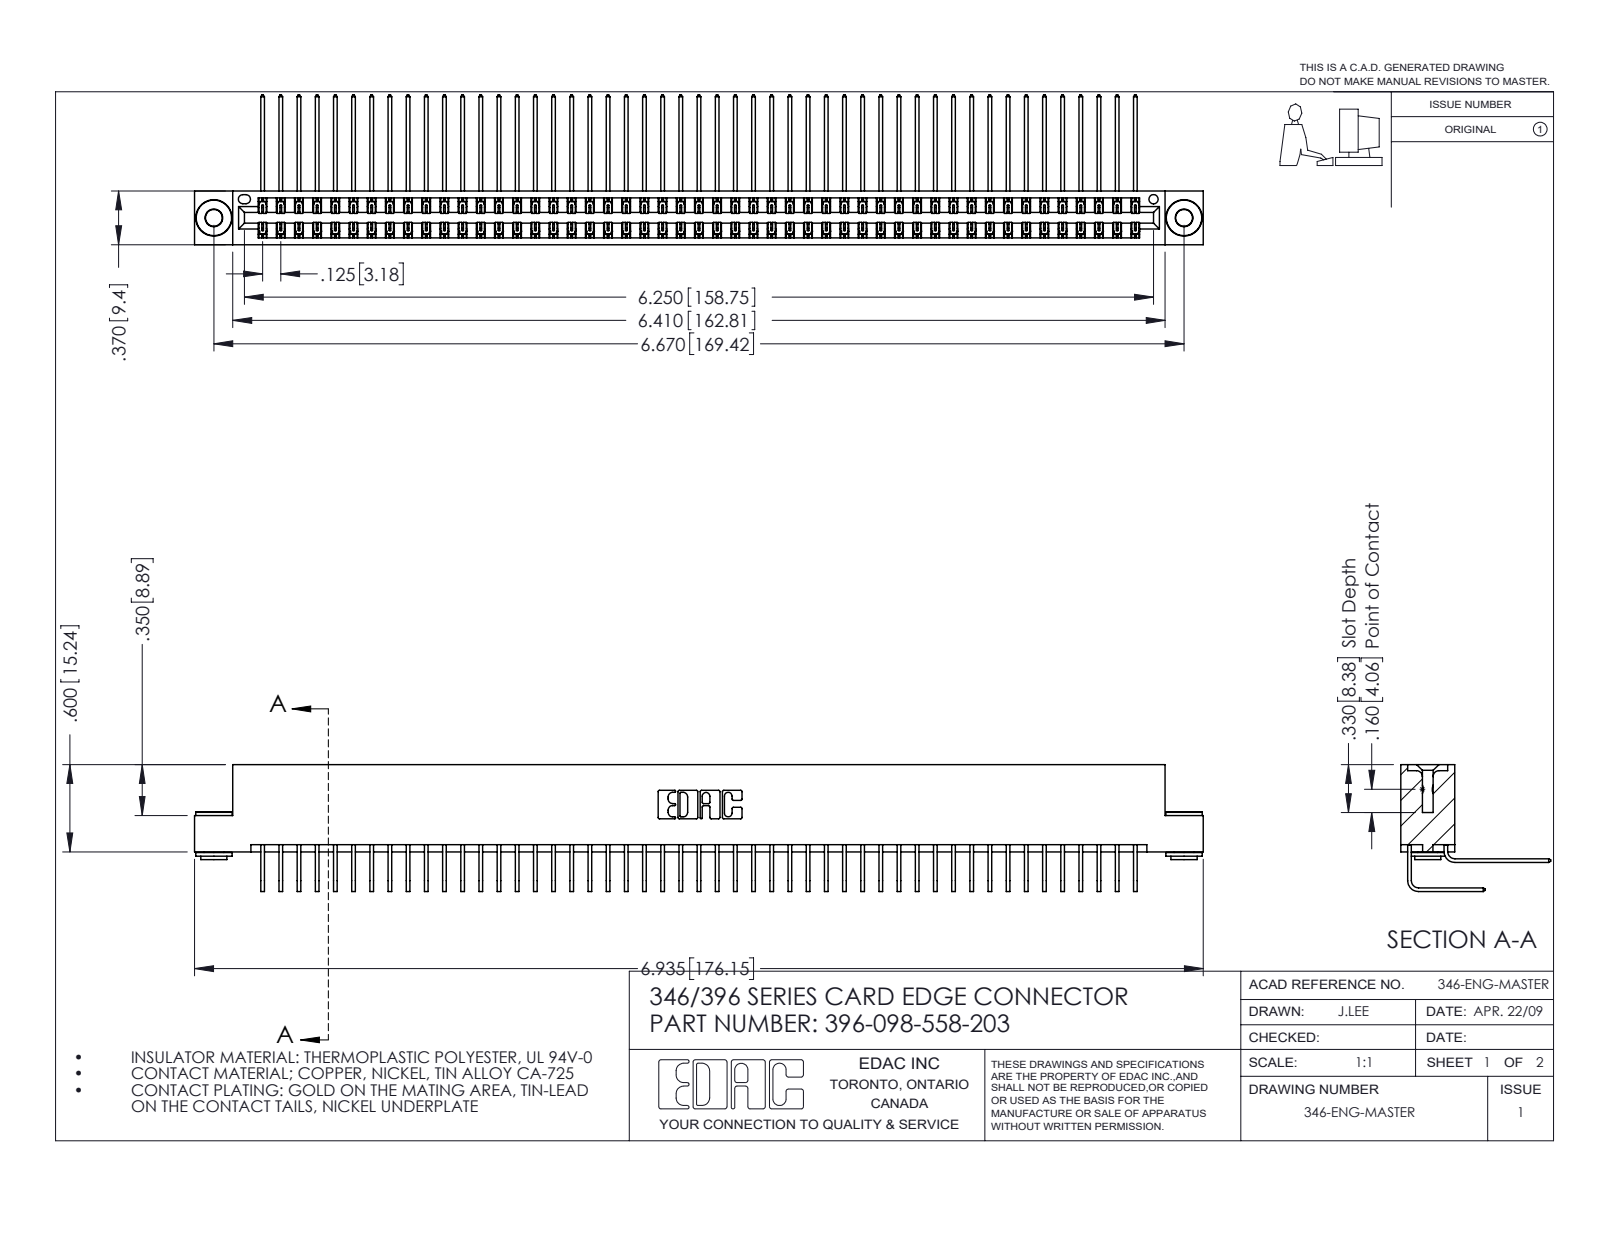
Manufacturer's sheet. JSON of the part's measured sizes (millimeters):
{"part_name": "346 Part_Flush Mounting Lugs - 0.156 Dia-TH; 345-292-001_558 Tail - 2; 345-292-001_558 559 Tail - 1; 345-250-002_345-250-002-102 (+1 more)", "step_written_by": "SolidWorks 2016 (CONFIG_CONTROL_DESIGN)", "units": "millimeters", "bodies": {"solids": 101, "faces": 5452, "planar": 3712, "cylindrical": 1732, "other": 8}, "overall_size": [176.1, 26.2, 22.2], "volume_mm3": 17810, "surface_area_mm2": 27520, "round_holes": [[2.9, 2], [4, 2], [1.6, 1]], "round_bosses_or_shafts": [[6.4, 2], [4.6, 2], [3.5, 2]], "partial_cylinders_radius": [[0.2, 147], [0.3, 22], [0.2, 6], [0.8, 6], [0.7, 3], [0.4, 2], [0.6, 2], [0.6, 2]], "face_to_face_distances": [8.2, 1.2, 0.6, 6.4, 9.4, 7.6, 1.8, 7, 3.8, 5.6], "hole_center_spacings": [6.2, 164.1, 169.4]}
